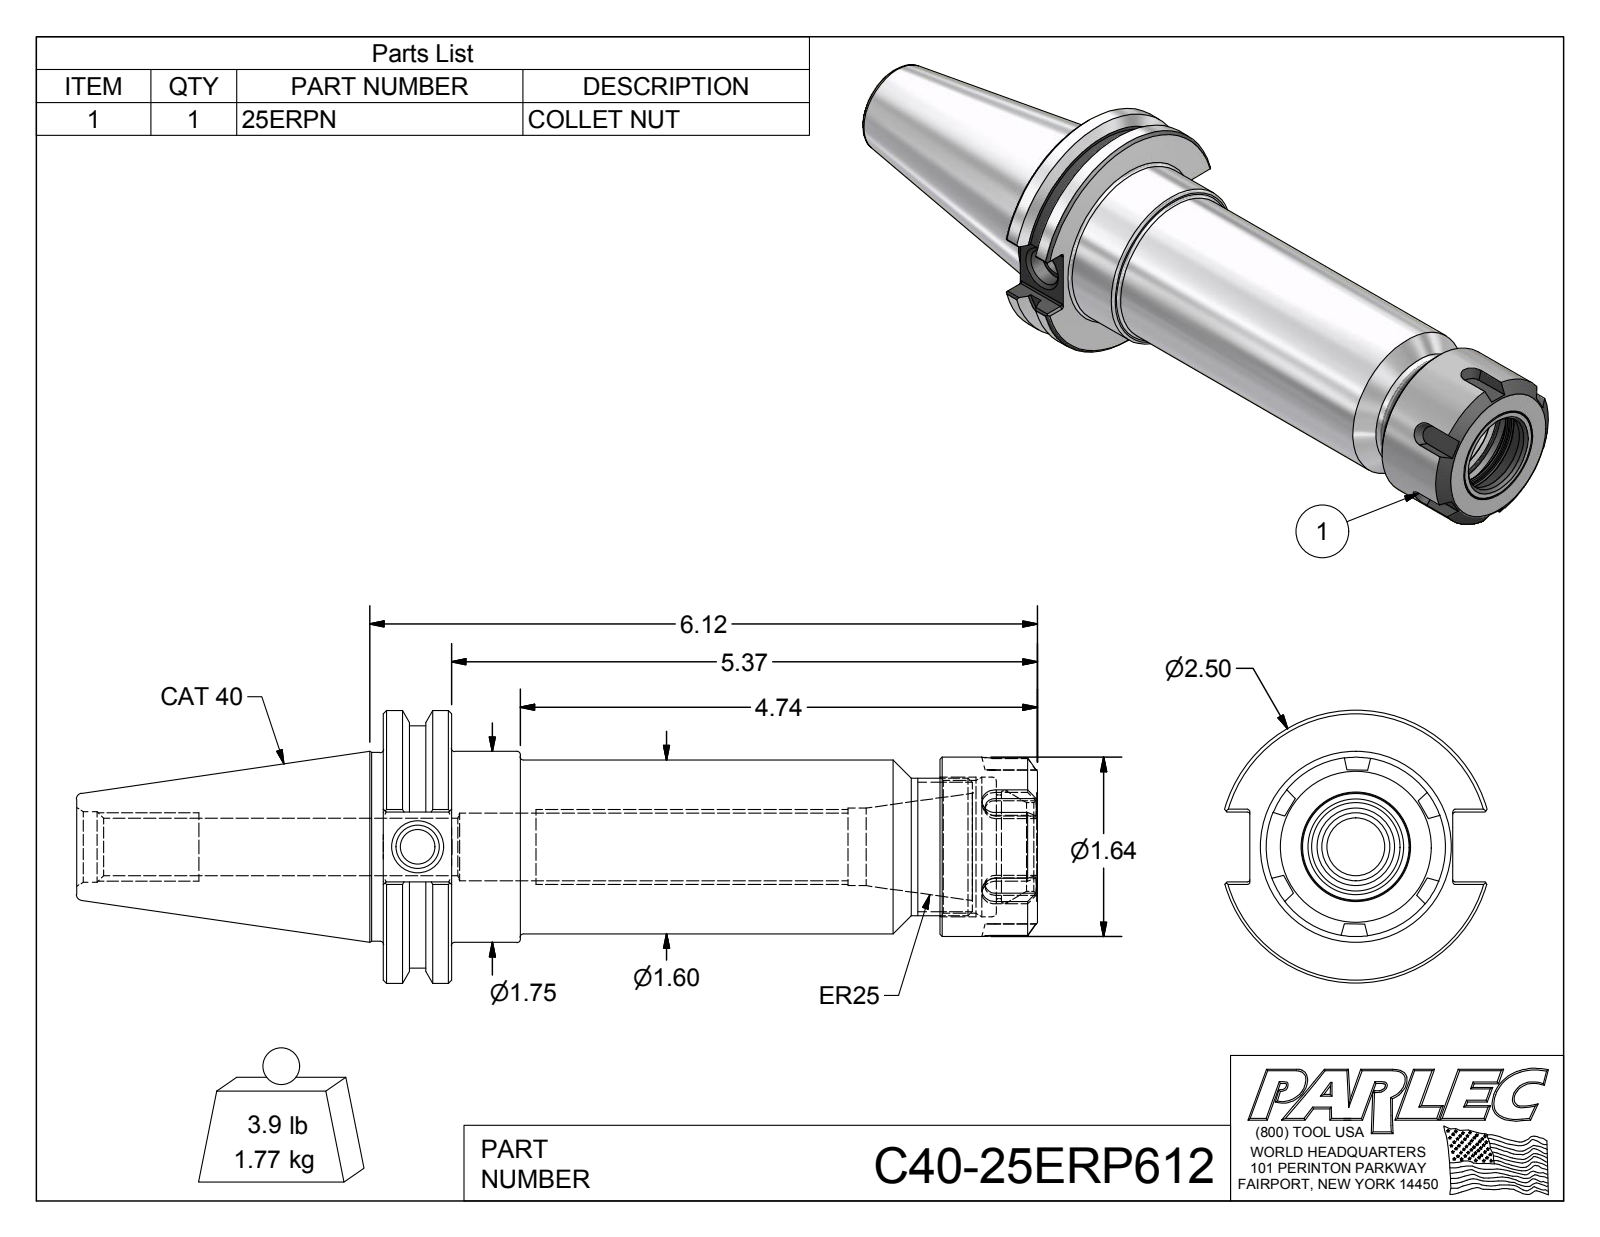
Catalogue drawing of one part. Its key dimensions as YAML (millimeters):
part_name: "C40-25ERP612; C40-25ER6-1; 25ERPN"
step_written_by: "Autodesk Inventor 2012 (AUTOMOTIVE_DESIGN)"
units: millimeters
bodies: {solids: 2, faces: 133, planar: 56, cylindrical: 34, other: 43}
overall_size: [223.7, 63.5, 61]
volume: 240100
surface_area: 48170
round_holes:
  - {diameter: 8, count: 1}
  - {diameter: 10.1, count: 1}
  - {diameter: 13.4, count: 1}
  - {diameter: 15.7, count: 1}
  - {diameter: 16.5, count: 1}
  - {diameter: 18, count: 1}
  - {diameter: 20.6, count: 1}
  - {diameter: 24.1, count: 1}
  - {diameter: 26.1, count: 1}
  - {diameter: 30.9, count: 1}
  - {diameter: 32.5, count: 1}
round_bosses_or_shafts:
  - {diameter: 63.5, count: 1}
  - {diameter: 56.4, count: 1}
  - {diameter: 44.5, count: 1}
  - {diameter: 43.9, count: 1}
  - {diameter: 41.7, count: 1}
  - {diameter: 40.5, count: 1}
  - {diameter: 32, count: 1}
partial_cylinders:
  - {radius: 0.5, count: 12}
face_to_face_distances: [15.9, 152.3, 136.4, 129.6, 113.7, 22.7, 142.7, 126.9, 13.2, 9.5]
